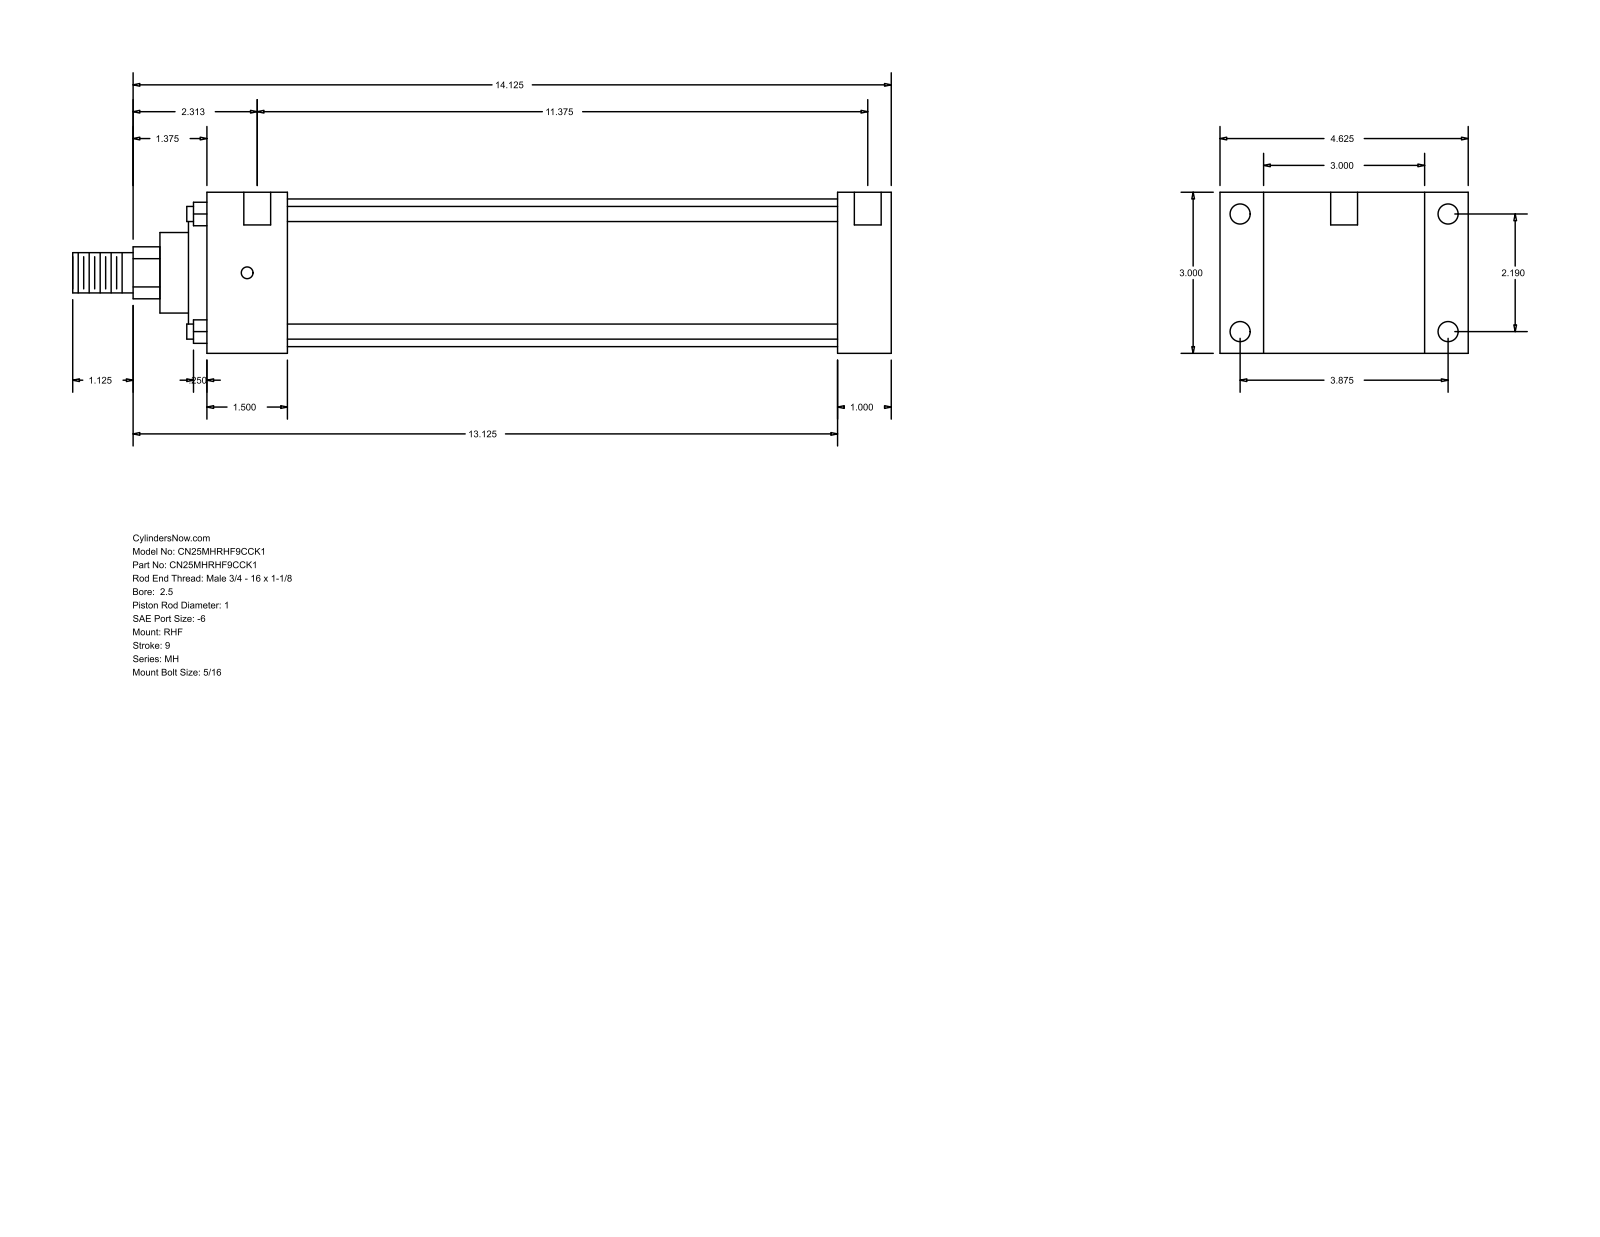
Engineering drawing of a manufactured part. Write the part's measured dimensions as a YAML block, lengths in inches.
part_name: "MH_RHF__0250_1"
step_written_by: "GSSL Pune (CONFIG_CONTROL_DESIGN)"
units: inches
bodies: {solids: 0, faces: 90, planar: 61, cylindrical: 29, other: 0}
overall_size: [15.25, 4.625, 3]
round_holes:
  - {diameter: 0.219, count: 4}
  - {diameter: 0.375, count: 4}
  - {diameter: 0.5, count: 2}
round_bosses_or_shafts:
  - {diameter: 0.281, count: 4}
  - {diameter: 2.75, count: 1}
  - {diameter: 2.375, count: 1}
  - {diameter: 1.5, count: 1}
  - {diameter: 1, count: 1}
  - {diameter: 0.75, count: 1}
partial_cylinders:
  - {radius: 0.484, count: 1}
face_to_face_distances: [3, 1, 0.813, 3.813, 12.75, 11.75, 4.625, 1.5, 10.25, 11.25]
hole_center_spacings: [2.19, 3.875, 4.451, 11.687, 0.125, 0.187, 11.375, 11.5]
